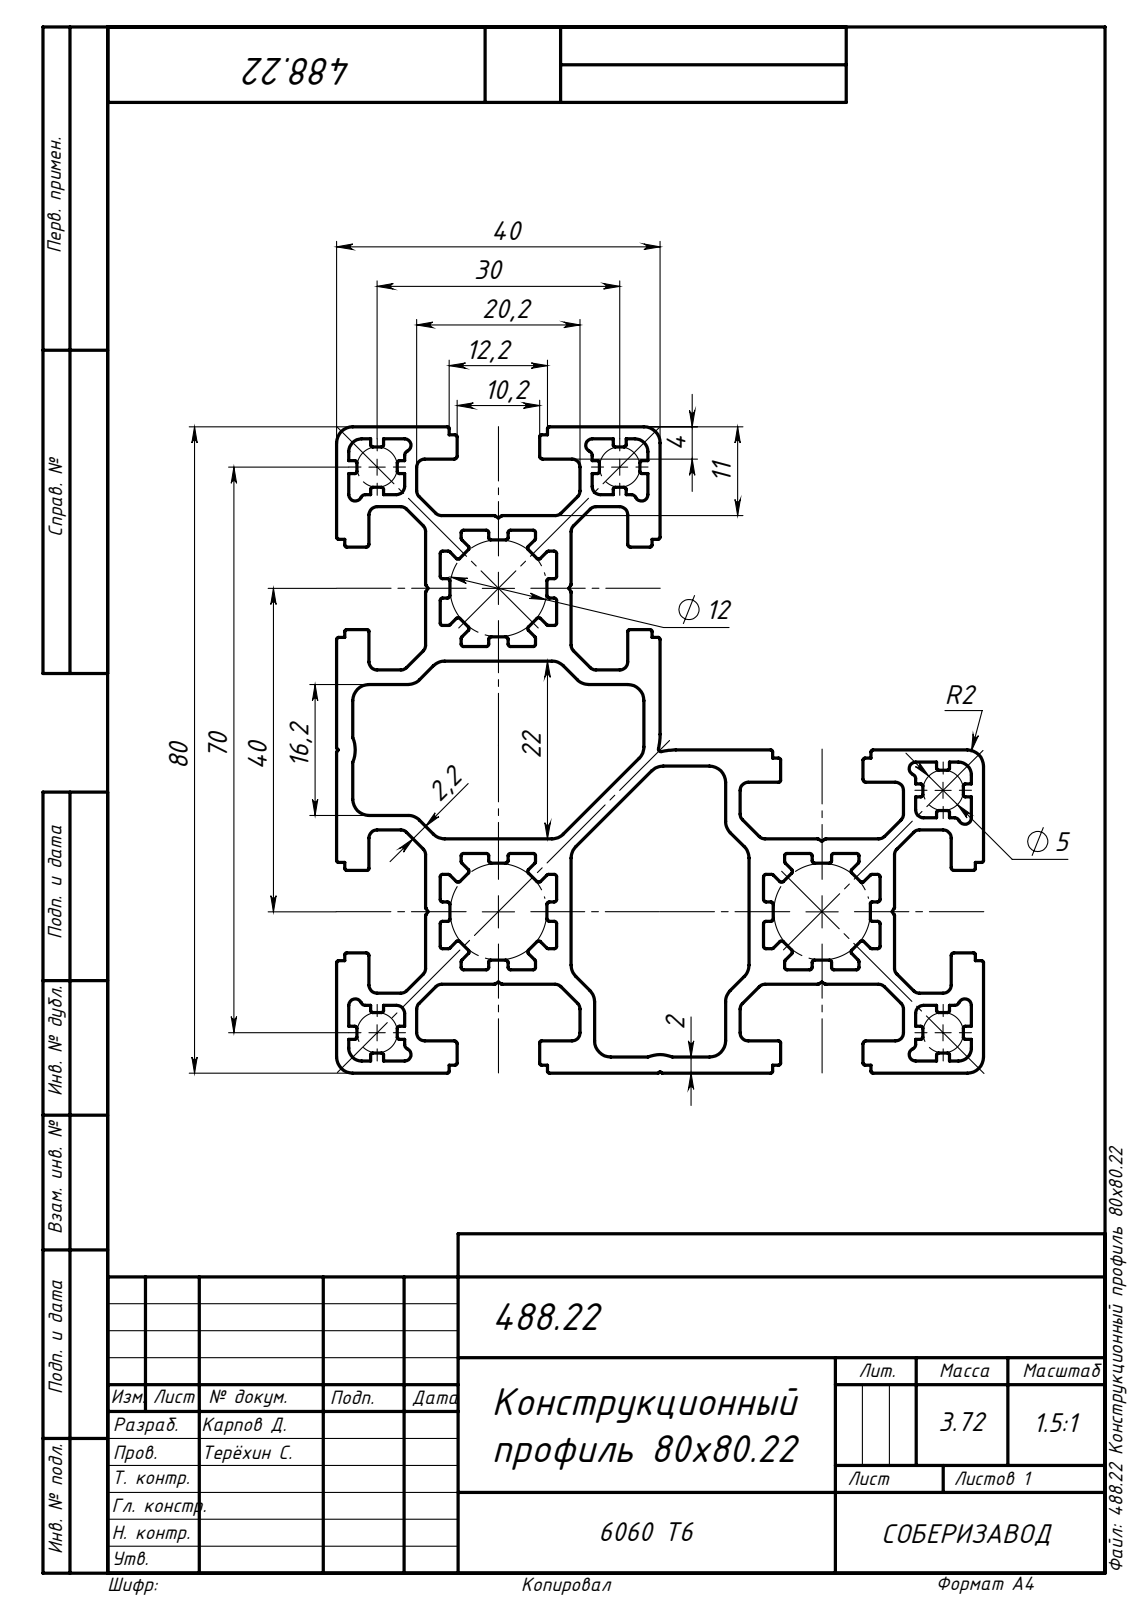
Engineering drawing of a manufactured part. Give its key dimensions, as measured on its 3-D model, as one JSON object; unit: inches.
{"part_name": "488.22 Конструкционный профиль 80х80.22", "step_written_by": "SolidWorks 2019 (AUTOMOTIVE_DESIGN)", "units": "inches", "bodies": {"solids": 1, "faces": 753, "planar": 399, "cylindrical": 354, "other": 0}, "overall_size": [39.37, 3.15, 3.15], "volume_in3": 84.09, "surface_area_in2": 1877, "partial_cylinders_radius": [[0.01, 114], [0.012, 101], [0.039, 53], [0.079, 27], [0.014, 10], [0.024, 10], [0.031, 10], [0.063, 5]], "face_to_face_distances": [1.575, 1.142, 0.433, 0.709, 2.008, 2.717, 0.752, 0.823, 0.157, 1.417]}
